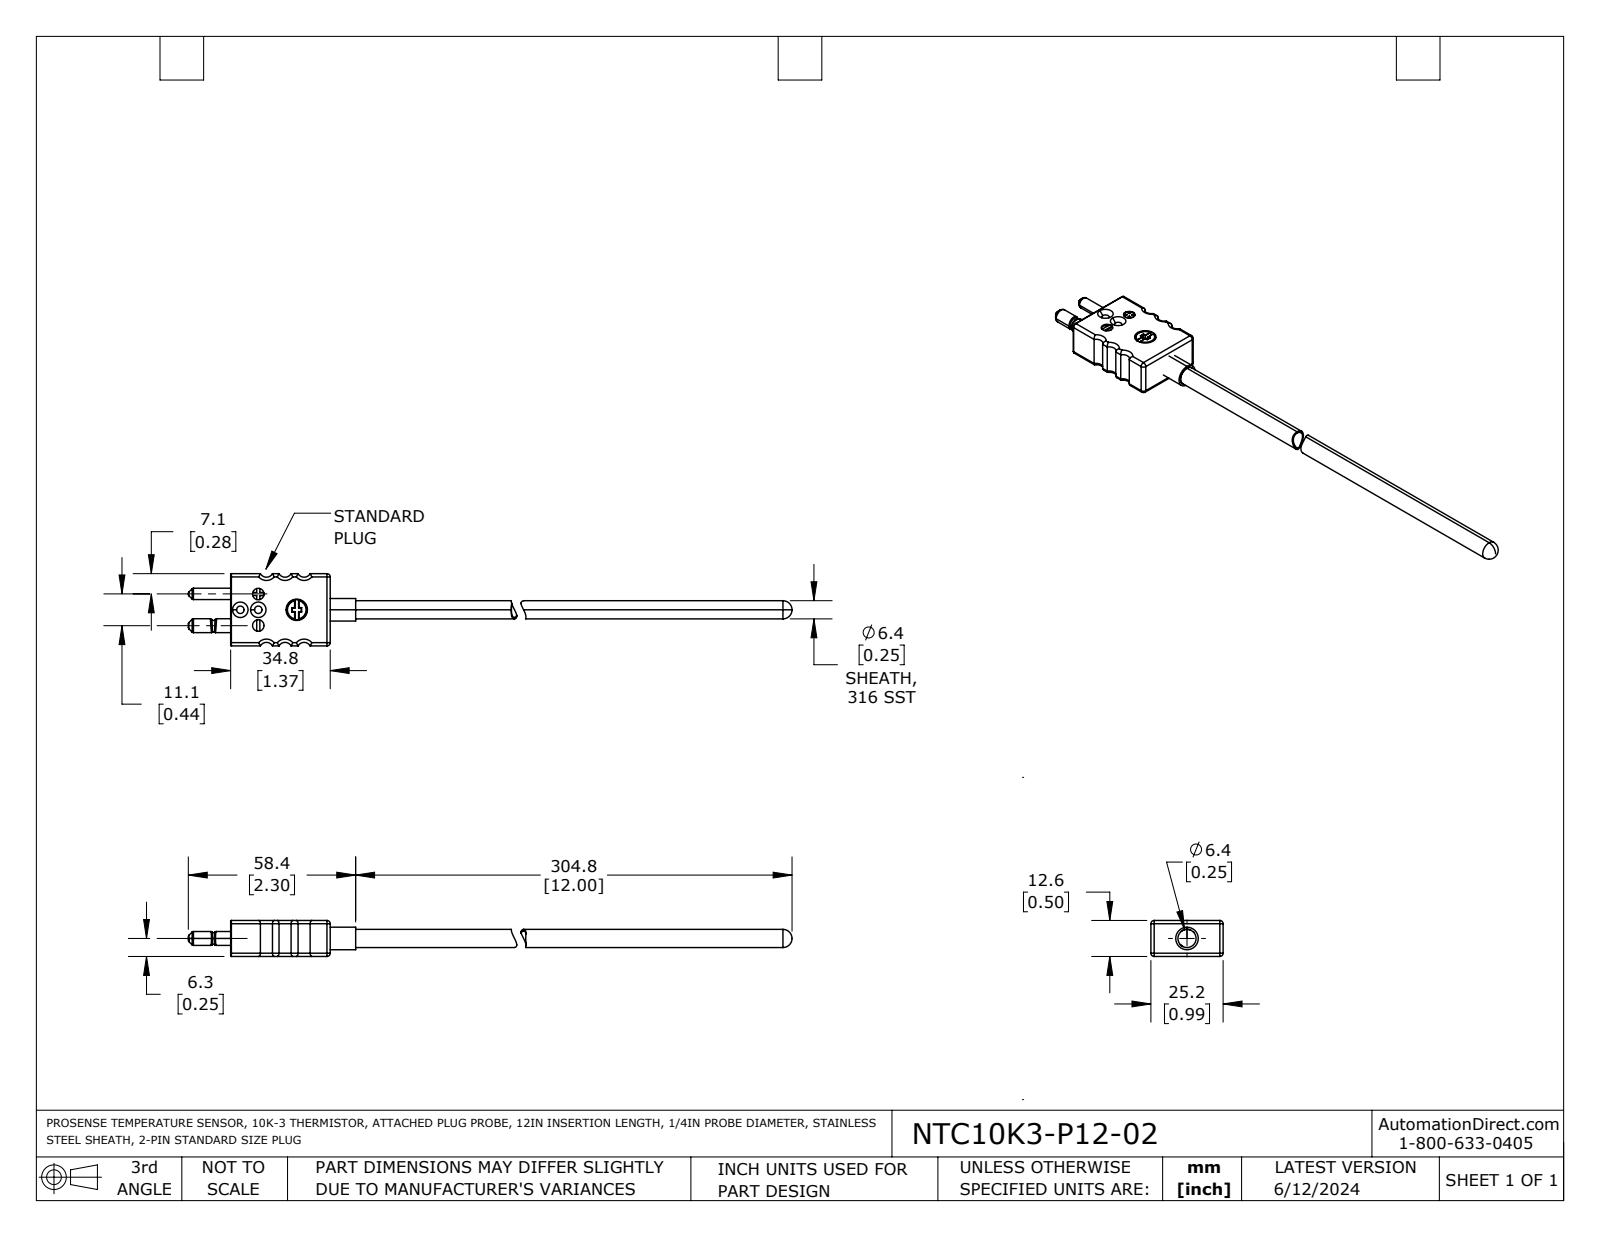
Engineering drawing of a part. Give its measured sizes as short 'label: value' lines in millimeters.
name: NTC10K3-P12-02
written by: SolidWorks 2021 (AUTOMOTIVE_DESIGN)
unit: mm
bodies: 3 solids, 201 faces (63 planar, 62 cylindrical, 76 other)
size: 363.1 × 25.2 × 12.6
volume: 13 700 mm³; area: 15 990 mm²
holes: 2× ⌀2.6, 2× ⌀4, 1× ⌀4.7, 1× ⌀5.3, 1× ⌀6.4, 1× ⌀7.5, 1× ⌀7.8
bosses: 1× ⌀7.9, 1× ⌀7.1, 1× ⌀6.4, 1× ⌀4.9, 1× ⌀4, 1× ⌀2.6
rounds: 8× R1.1, 6× R2.4, 4× R0.3
face distances: 12.6, 25.2, 34.8, 1.3, 7.6, 17.6, 10, 1.3, 11.3, 6.9
hole spacings: 5.5, 8.3, 14.5, 6.3, 11, 13.4, 19.7
